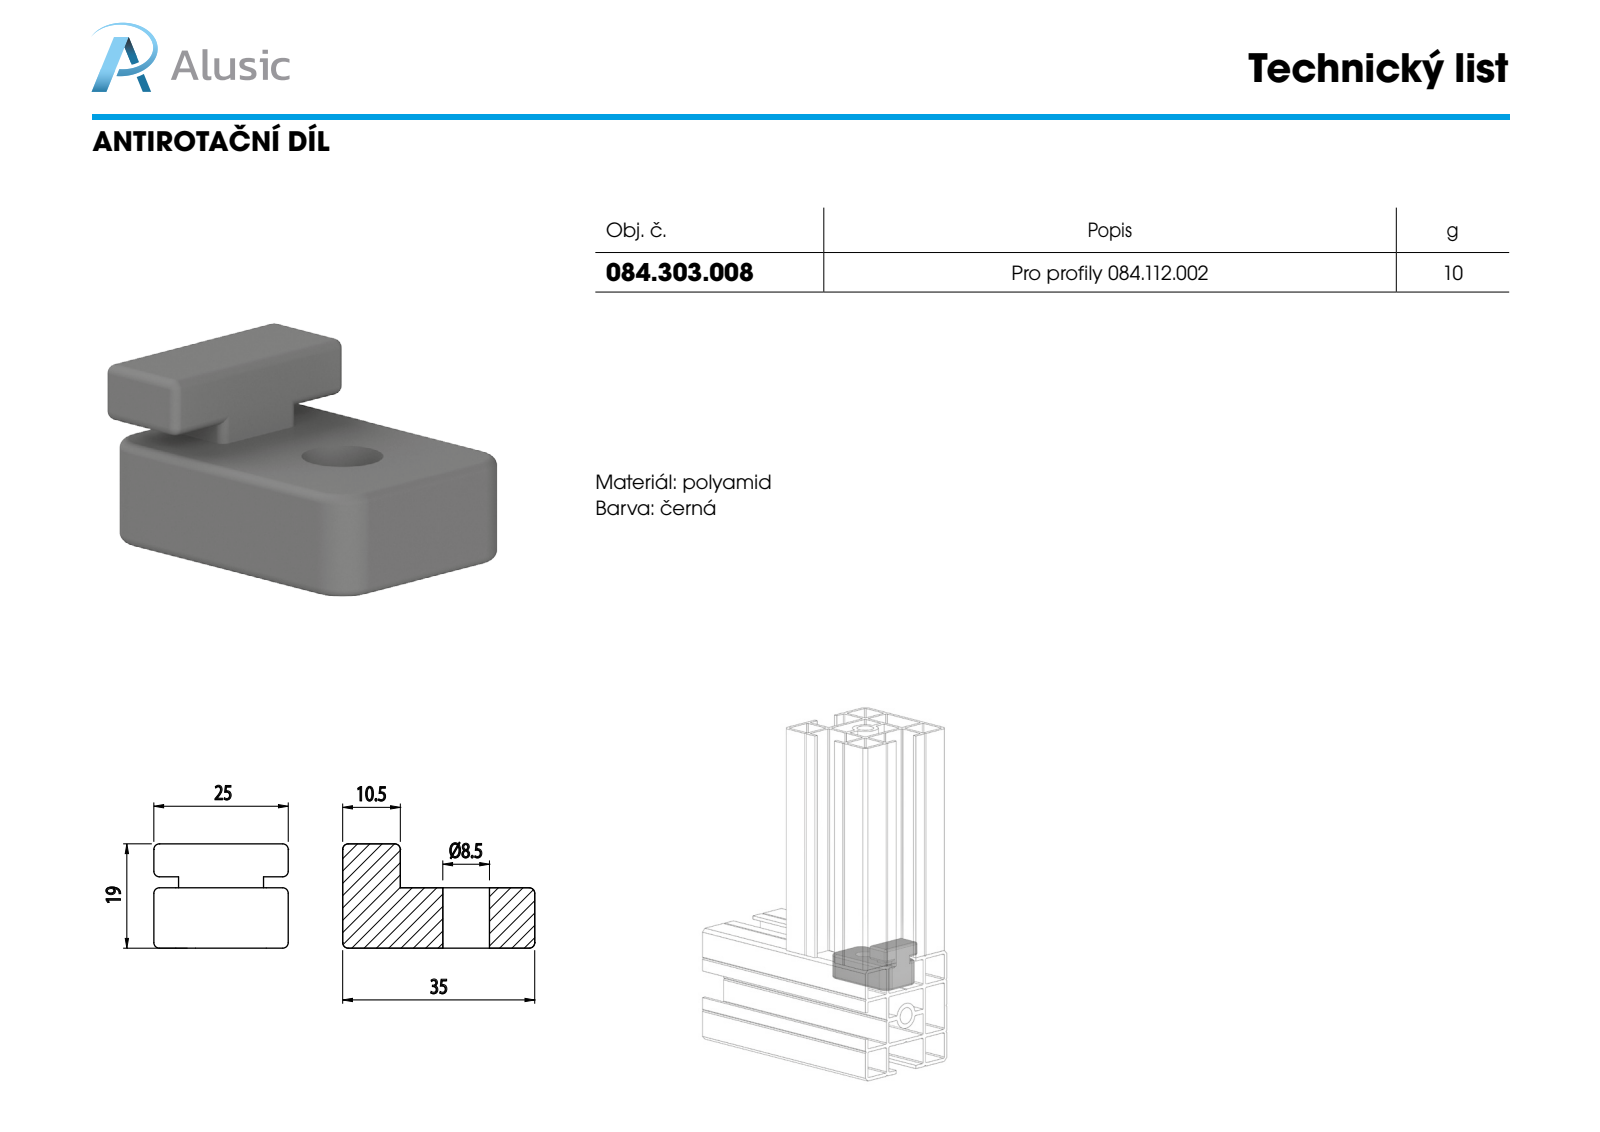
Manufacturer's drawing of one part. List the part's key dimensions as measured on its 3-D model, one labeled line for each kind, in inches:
Part name (STEP PRODUCT): 084.303.008
STEP written by: SolidWorks 2012 (CONFIG_CONTROL_DESIGN)
Units: inches
Bodies: 1 solid, 140 faces (26 planar, 68 cylindrical, 46 other)
Overall size (bounding box): 1.378 × 0.984 × 0.748
Volume: 0.477 in³ · Surface area: 7.578 in²
Round holes (diameter × count): ⌀0.276 ×1
Partial cylindrical surfaces — rounded edges, fillets, slot ends (radius × count): R0.039 ×48, R0.157 ×4, R0.256 ×1
Main face-to-face distances: 0.118, 0.433, 0.315, 0.748, 0.866, 0.984, 0.551, 1.378, 1.26, 0.965
